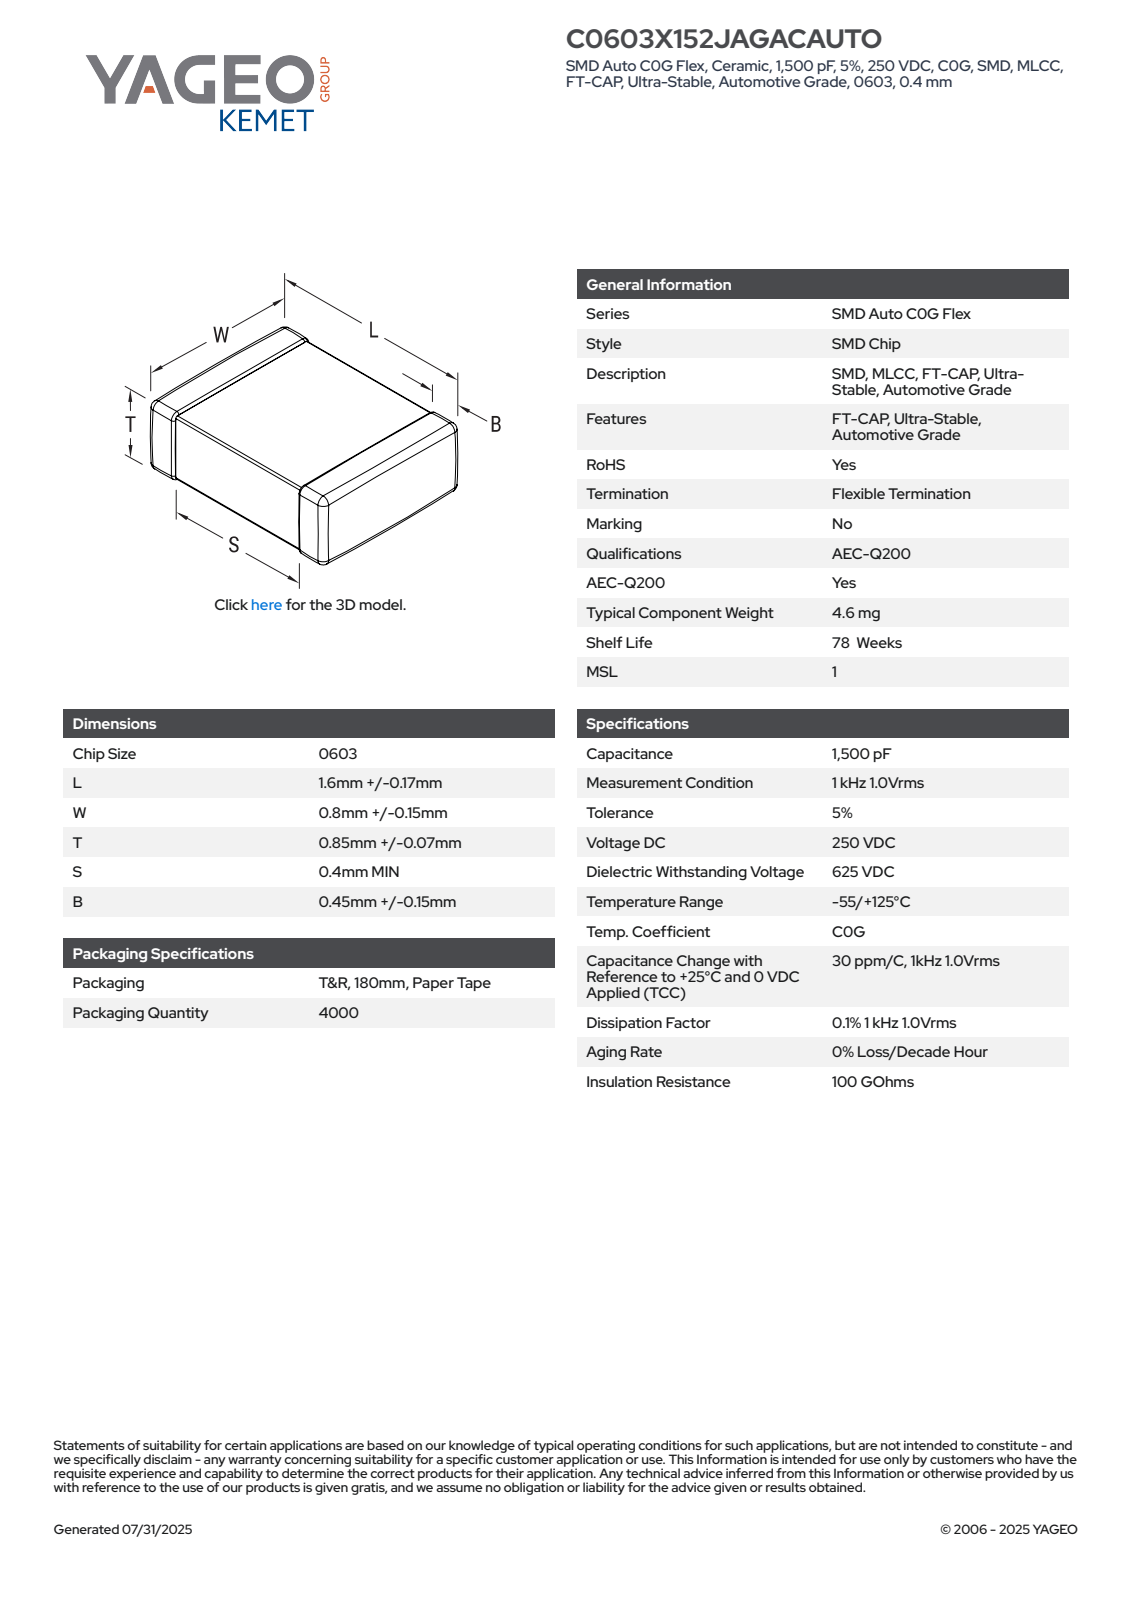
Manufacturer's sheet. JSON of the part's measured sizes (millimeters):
{"part_name": "CCS_CCSTD_0603_L1.77W0.95T0.92B0.45", "step_written_by": "SolidWorks 2021 (AUTOMOTIVE_DESIGN)", "units": "millimeters", "bodies": {"solids": 4, "faces": 125, "planar": 71, "cylindrical": 38, "other": 16}, "overall_size": [1.77, 0.95, 0.92], "volume_mm3": 2, "surface_area_mm2": 8, "face_to_face_distances": [0.9, 0.92, 0.95, 0.93, 1.77, 0.91, 0.88, 0.89, 0.82, 0.96]}
